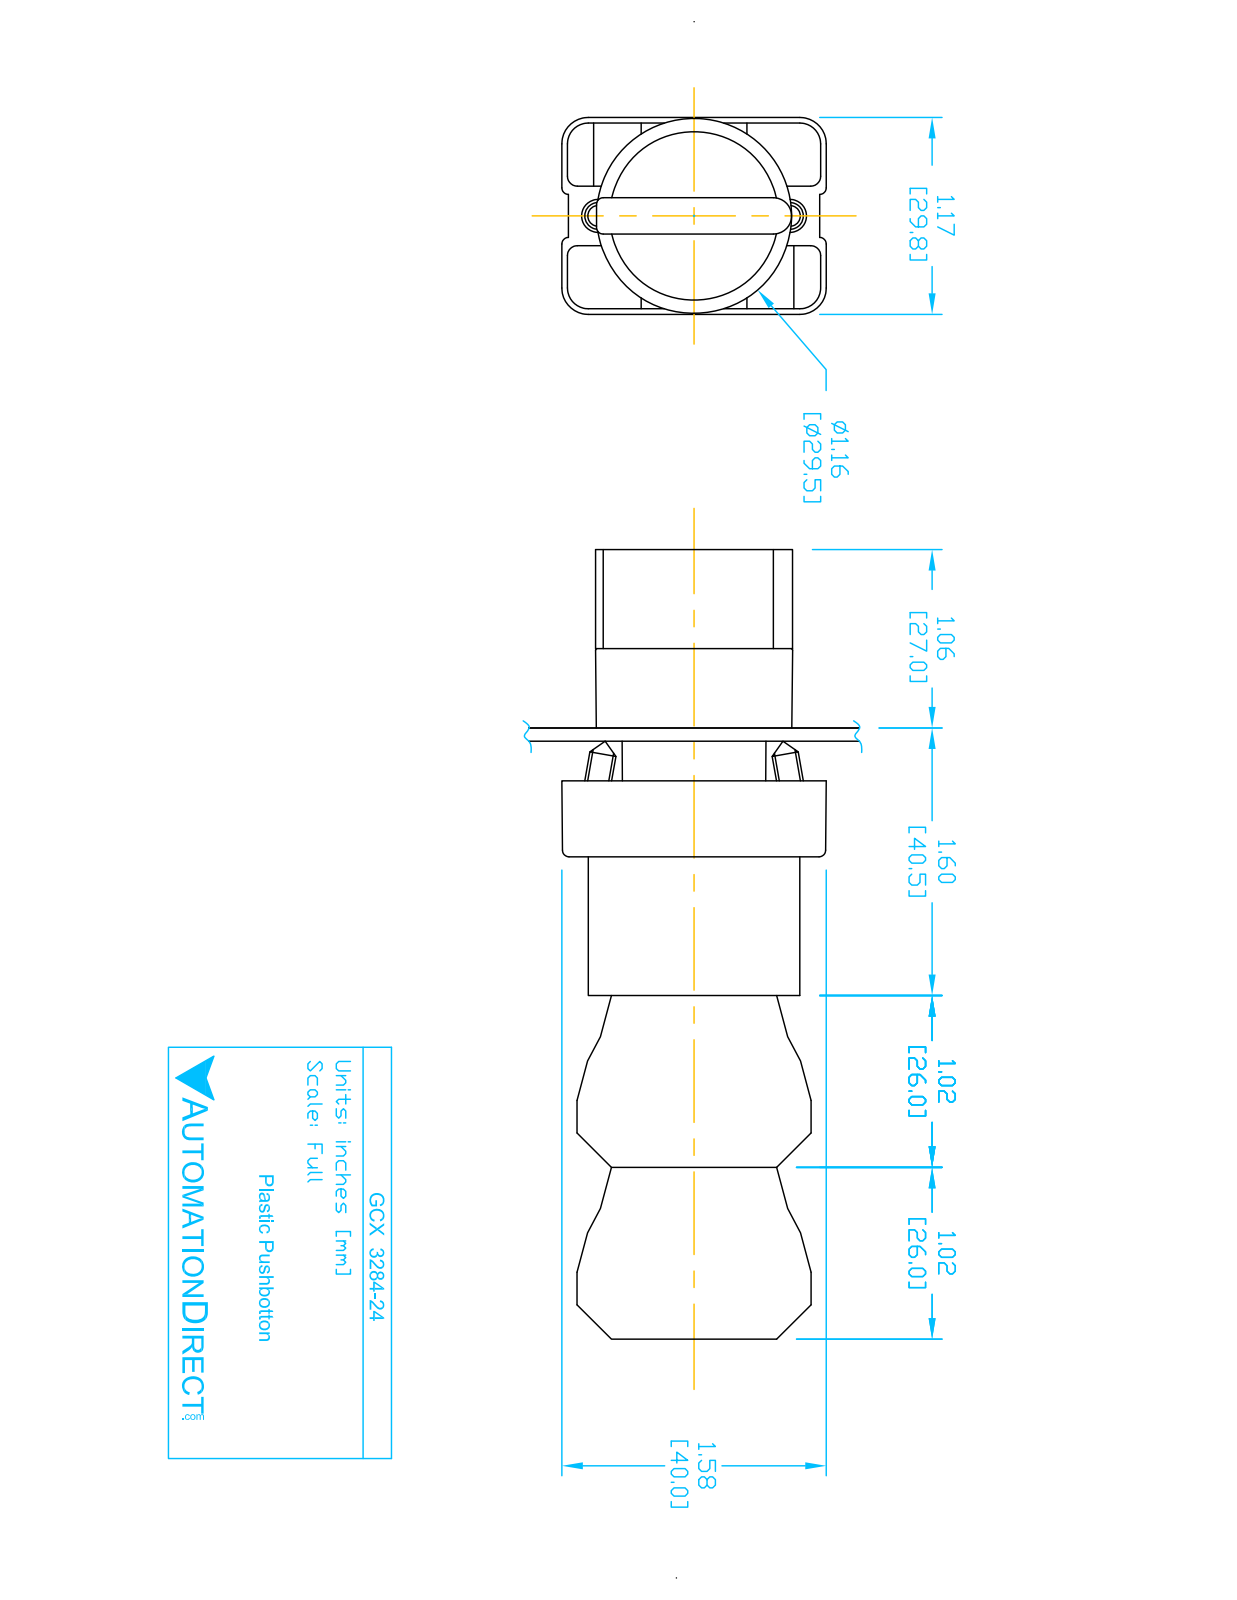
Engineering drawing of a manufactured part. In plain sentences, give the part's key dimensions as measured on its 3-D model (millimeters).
The part is named "ecx1030; ECX1050; GCX3284 OPERATOR; ECX3029-2 (+2 more)". Its 3-D file was written by "SolidWorks 2016 (AUTOMOTIVE_DESIGN)". It is 11 solids with 724 faces: 488 planar, 193 cylindrical and 43 other. Overall it measures 118.8 by 40.2 by 29.9 millimeters. Its volume is 77 850 cubic millimeters and its surface area 38 210 square millimeters. Round holes: 4 of diameter 2, 2 of diameter 2.2, 2 of diameter 3.1, 2 of diameter 3.3, 1 of diameter 5, 1 of diameter 11.9, 1 of diameter 22.3, 1 of diameter 22.6, 1 of diameter 26. Round bosses or shafts: 4 of diameter 4, 1 of diameter 29.8, 1 of diameter 25.5, 1 of diameter 24, 1 of diameter 21.7, 1 of diameter 19.8, 1 of diameter 12.8. Partial cylindrical surfaces (rounded edges, fillets, slot ends): 24 of radius 1.5, 12 of radius 1, 12 of radius 3.1, 12 of radius 4, 9 of radius 1, 2 of radius 0.5, 2 of radius 1.6, 2 of radius 2. The main face-to-face distances are 14.7, 15.1, 26, 29.7, 0.4, 21, 47, 77.3, 51.3, 30.3. The hole center spacings are 6, 25.5, 24.7, 12, 13.7, 13.8, 27.5, 12.3.
